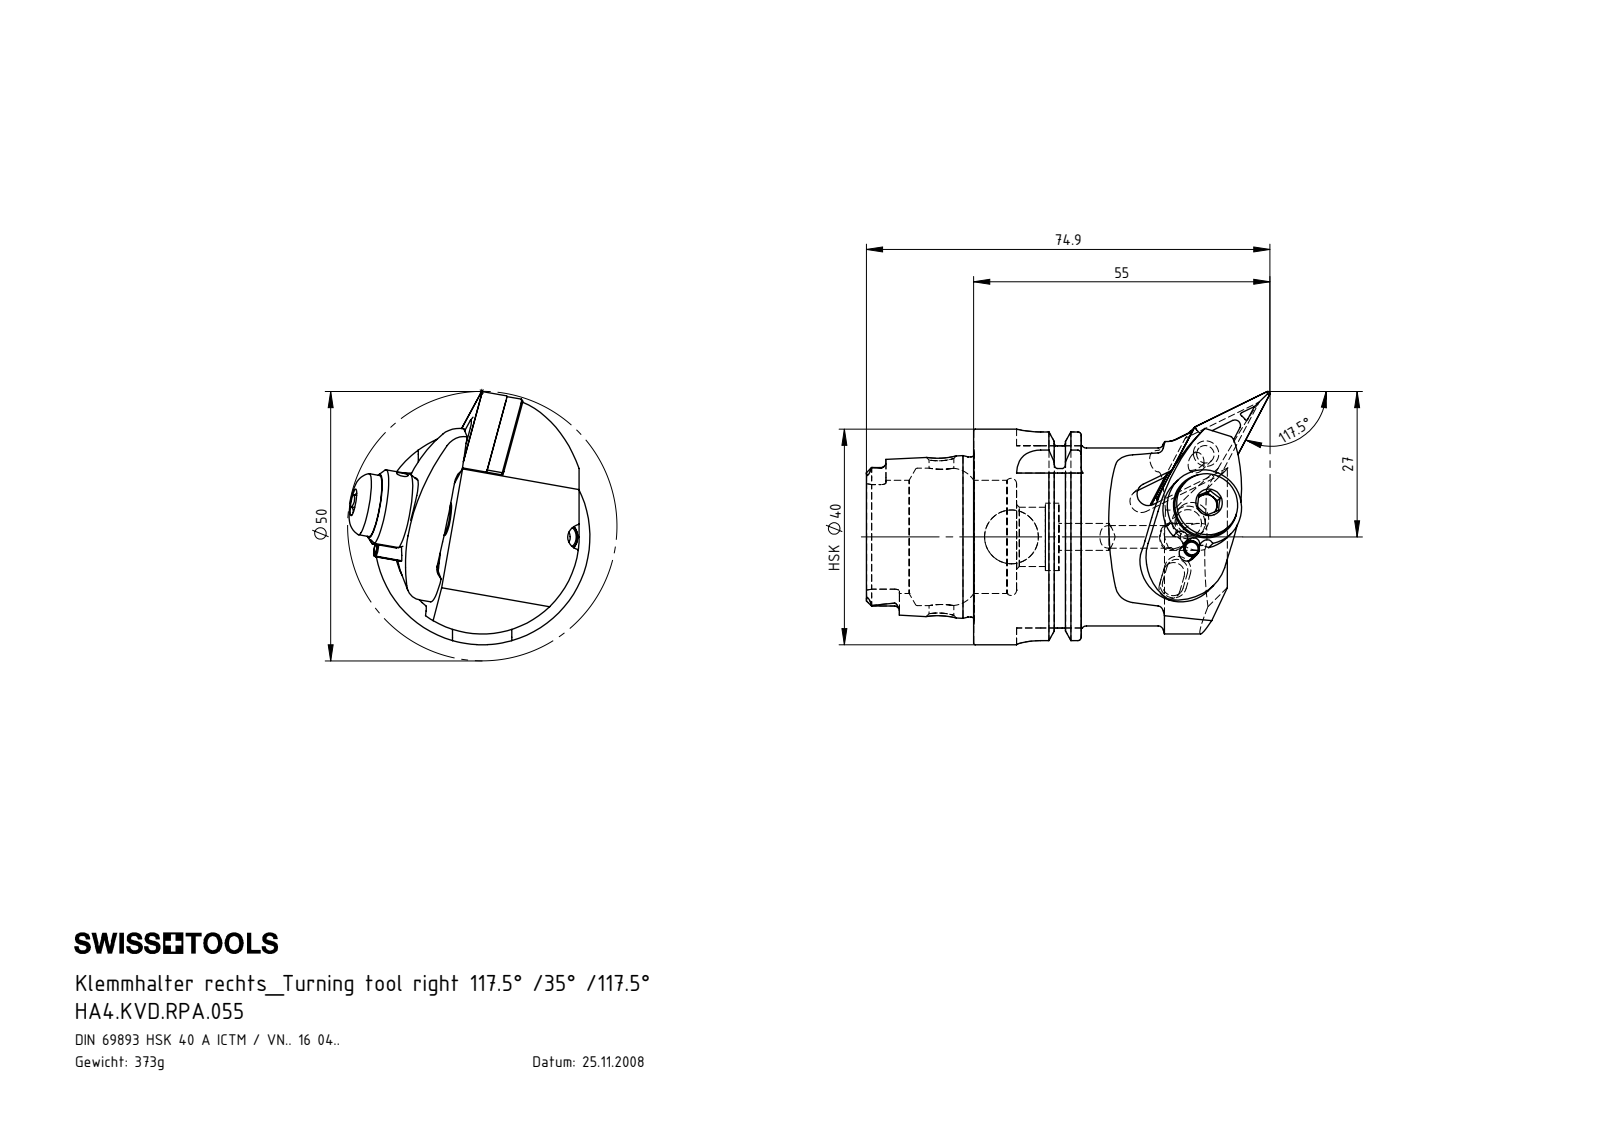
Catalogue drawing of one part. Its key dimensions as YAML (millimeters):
part_name: "WCC-ER2.001.010_A; KVT_MB_600_050; WCC-ER3.102.024_C; WVD-ER2.101.003_A (+7 more)"
step_written_by: "SolidWorks 2017 (AUTOMOTIVE_DESIGN)"
units: millimeters
bodies: {solids: 11, faces: 467, planar: 126, cylindrical: 154, other: 187}
overall_size: [74.9, 47, 45.65]
volume: 46976
surface_area: 18586
round_holes:
  - {diameter: 2, count: 3}
  - {diameter: 5, count: 3}
  - {diameter: 7, count: 2}
  - {diameter: 2.4, count: 1}
  - {diameter: 3, count: 1}
  - {diameter: 3.3, count: 1}
  - {diameter: 3.8, count: 1}
  - {diameter: 4, count: 1}
  - {diameter: 4.2, count: 1}
  - {diameter: 4.6, count: 1}
  - {diameter: 4.95, count: 1}
  - {diameter: 6.2, count: 1}
round_bosses_or_shafts:
  - {diameter: 5, count: 2}
  - {diameter: 3, count: 2}
  - {diameter: 40, count: 1}
  - {diameter: 34.75, count: 1}
  - {diameter: 33, count: 1}
  - {diameter: 29.71, count: 1}
  - {diameter: 14, count: 1}
  - {diameter: 11.5, count: 1}
partial_cylinders:
  - {radius: 0.39, count: 6}
  - {radius: 0.9, count: 6}
  - {radius: 0.4, count: 4}
  - {radius: 4.5, count: 4}
  - {radius: 0.69, count: 3}
  - {radius: 0.69, count: 3}
  - {radius: 1.5, count: 3}
  - {radius: 17, count: 3}
face_to_face_distances: [7.63, 3.18, 4.45, 9.53, 9.12, 7.95, 12, 8.93, 5.75, 1.3]
hole_center_spacings: [22.32, 8.01, 8.02, 8.03, 8.04, 8.19, 8.2, 14.12]
